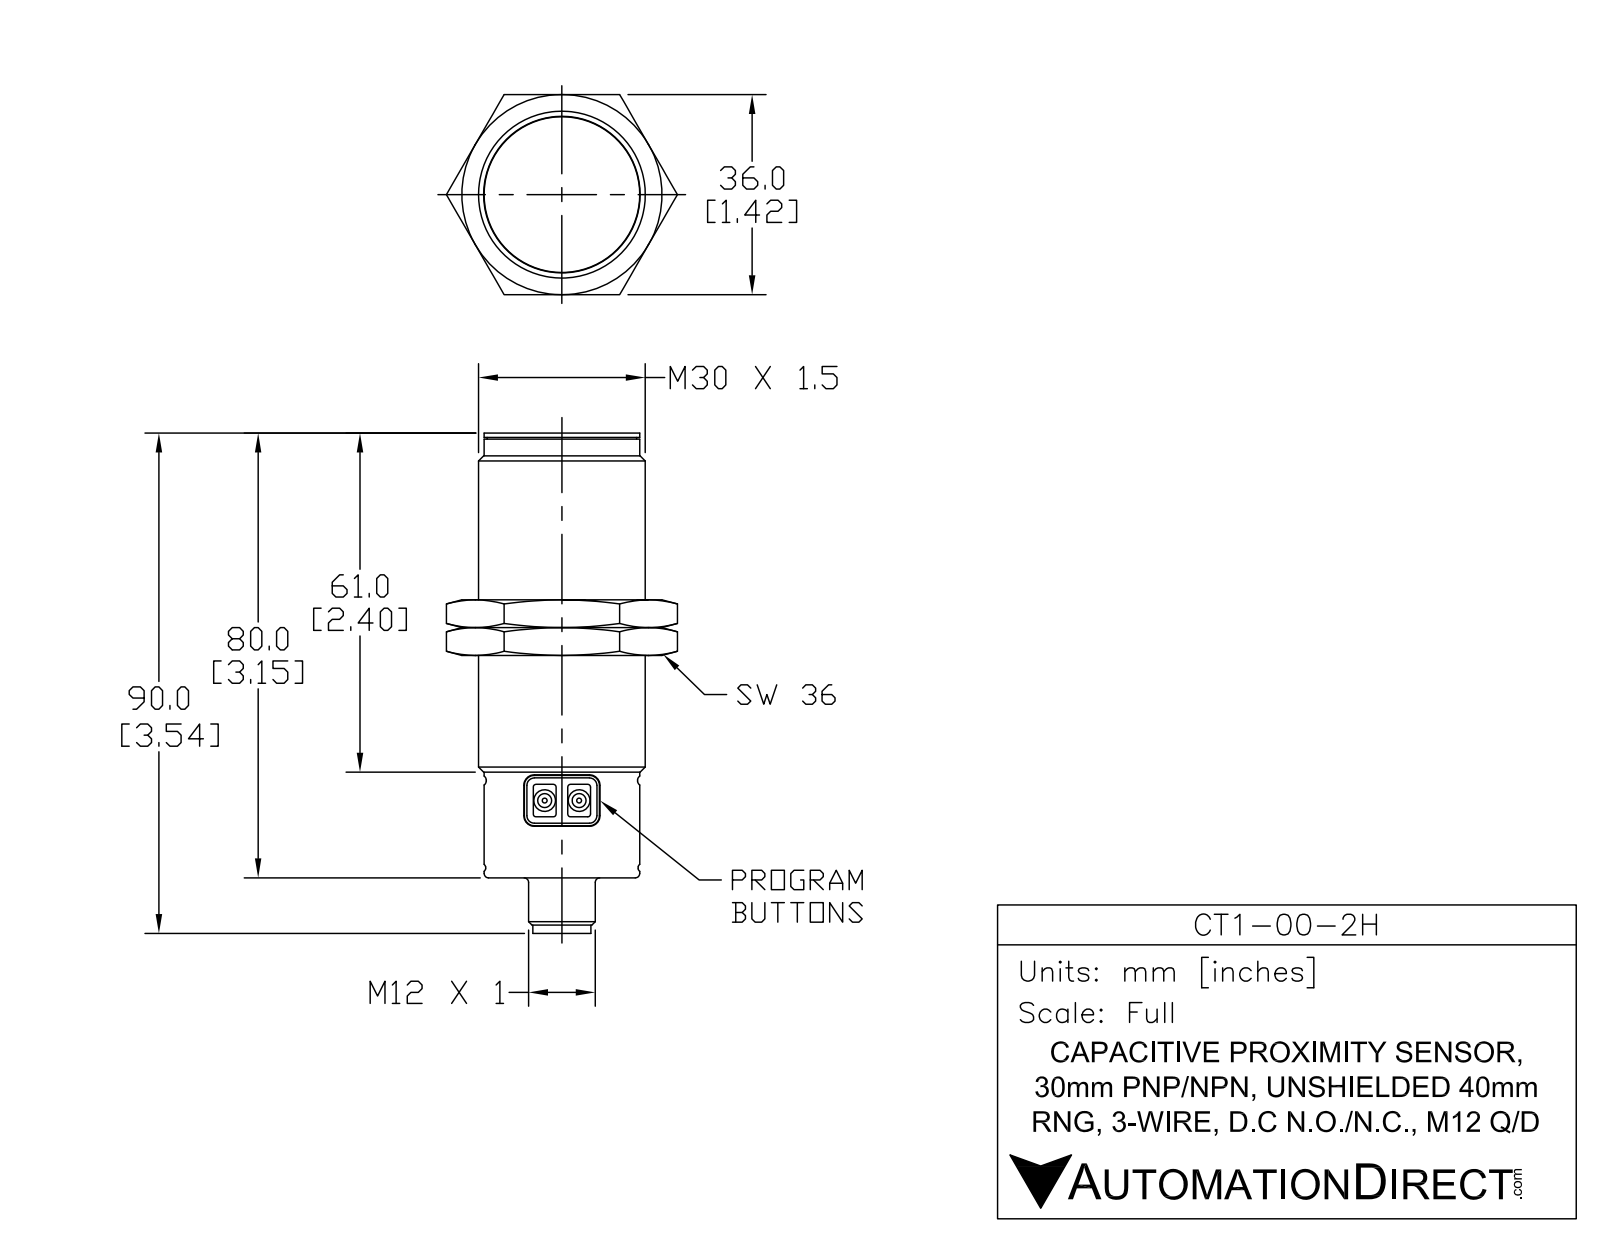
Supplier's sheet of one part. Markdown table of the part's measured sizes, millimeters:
| quantity | value |
| --- | --- |
| part name | CT1-00-2H |
| STEP written by | SolidWorks 2017 (AUTOMOTIVE_DESIGN) |
| units | millimeters |
| bodies | 3 solids, 177 faces (54 planar, 53 cylindrical, 70 other) |
| overall size | 90 × 41.6 × 36 |
| volume | 59 260 mm³ |
| surface area | 13 250 mm² |
| round holes (diameter × count) | 8.4 × 1, 28.9 × 1 |
| round bosses / shafts (diameter × count) | 2.5 × 2, 30 × 1, 28 × 1, 26.9 × 1, 12 × 1, 10.4 × 1 |
| partial cylindrical surfaces (radius × count) | 0.5 × 8, 0.4 × 4, 1.9 × 4, 0.8 × 2, 1 × 2, 0.6 × 1 |
| main face-to-face distances | 40, 5, 35, 36, 45, 80, 30, 10, 50, 1.2 |
